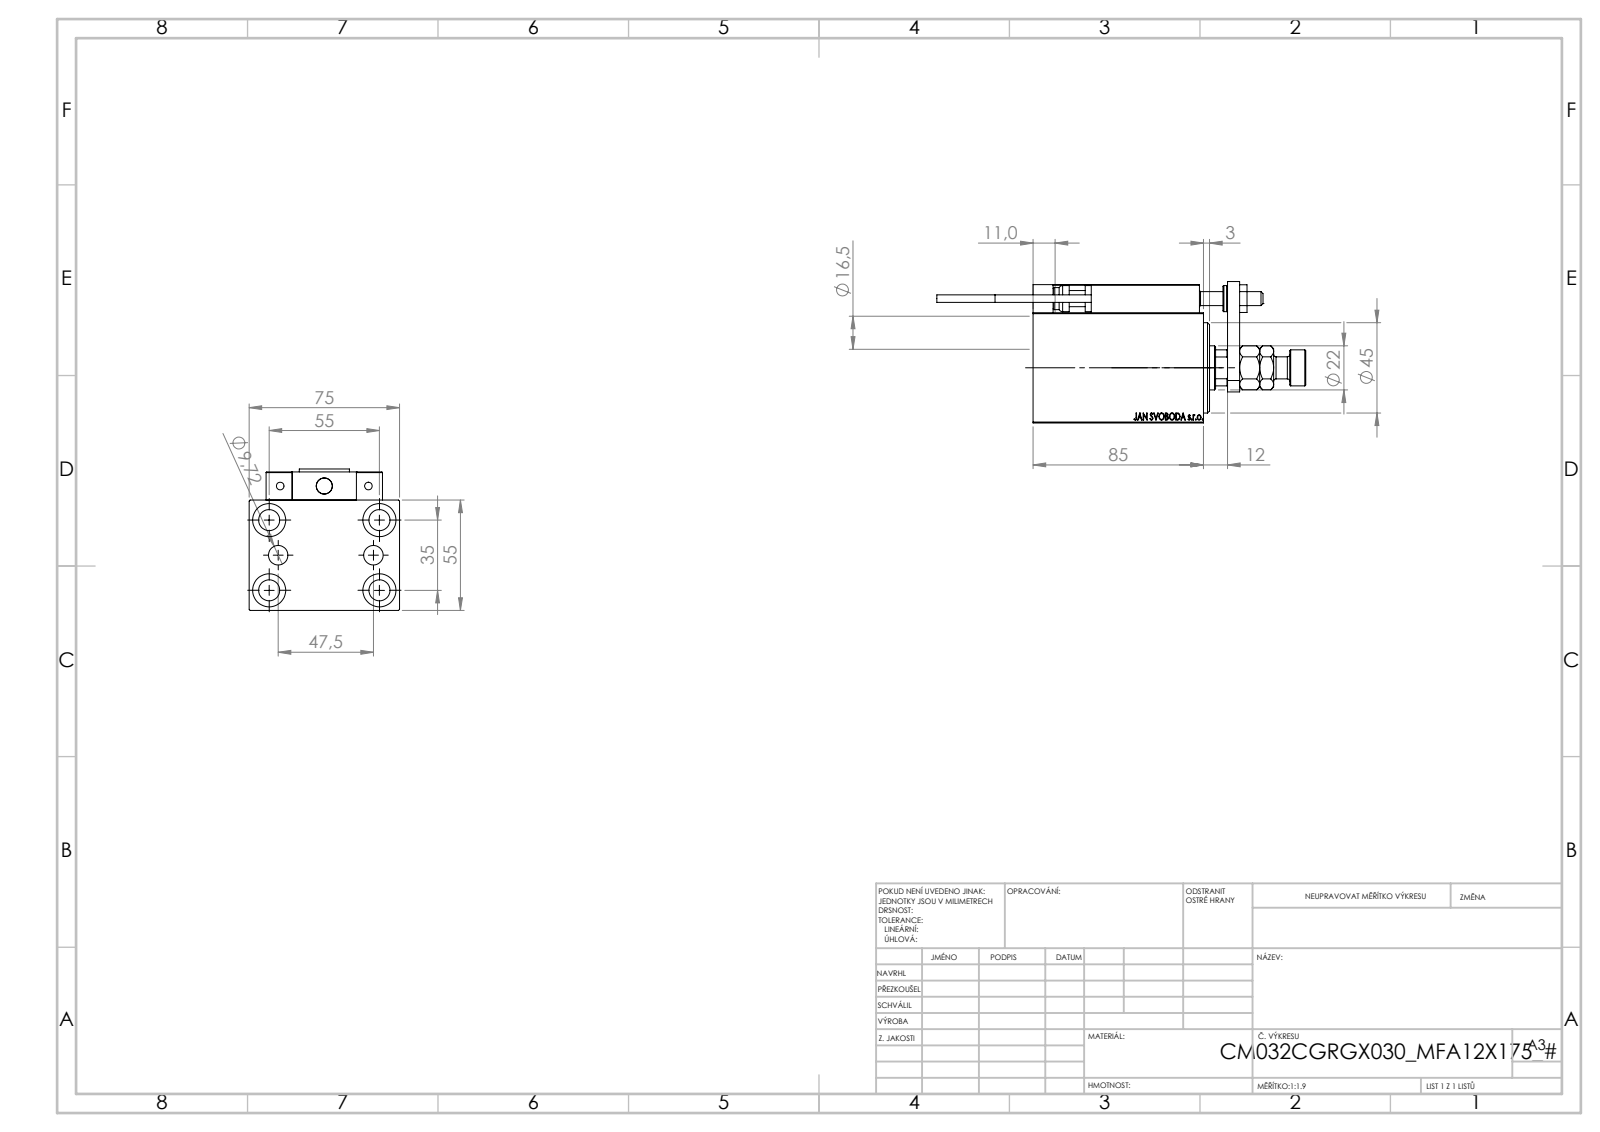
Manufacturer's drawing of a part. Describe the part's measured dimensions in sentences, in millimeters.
The part is named "ALLEN BOLT D5; SWITCH_X_FRONT_BACK; MAGNET; KONCOVKA (+7 more)". Its 3-D file was written by "SolidWorks 2019 (CONFIG_CONTROL_DESIGN)". It is 24 solids with 1330 faces: 576 planar, 188 cylindrical and 566 other. Overall it measures 184 by 75 by 70.5 millimeters. Its volume is 355 862 cubic millimeters and its surface area 90 099 square millimeters. Round holes: 6 of diameter 4, 5 of diameter 8, 5 of diameter 10.5, 5 of diameter 16.5, 4 of diameter 3.2, 2 of diameter 5, 2 of diameter 9.72, 1 of diameter 7, 1 of diameter 22, 1 of diameter 25.5, 1 of diameter 32, 1 of diameter 34. Round bosses or shafts: 2 of diameter 11, 2 of diameter 5, 2 of diameter 3.8, 1 of diameter 18, 1 of diameter 13. Partial cylindrical surfaces (rounded edges, fillets, slot ends): 30 of radius 0.3, 2 of radius 3, 1 of radius 10.5. The main face-to-face distances are 55, 75, 14, 69, 5, 18, 3, 25, 23, 10. The hole center spacings are 17.9, 32.6, 54.16, 11.37, 20, 23.75, 29.59, 29.69.
